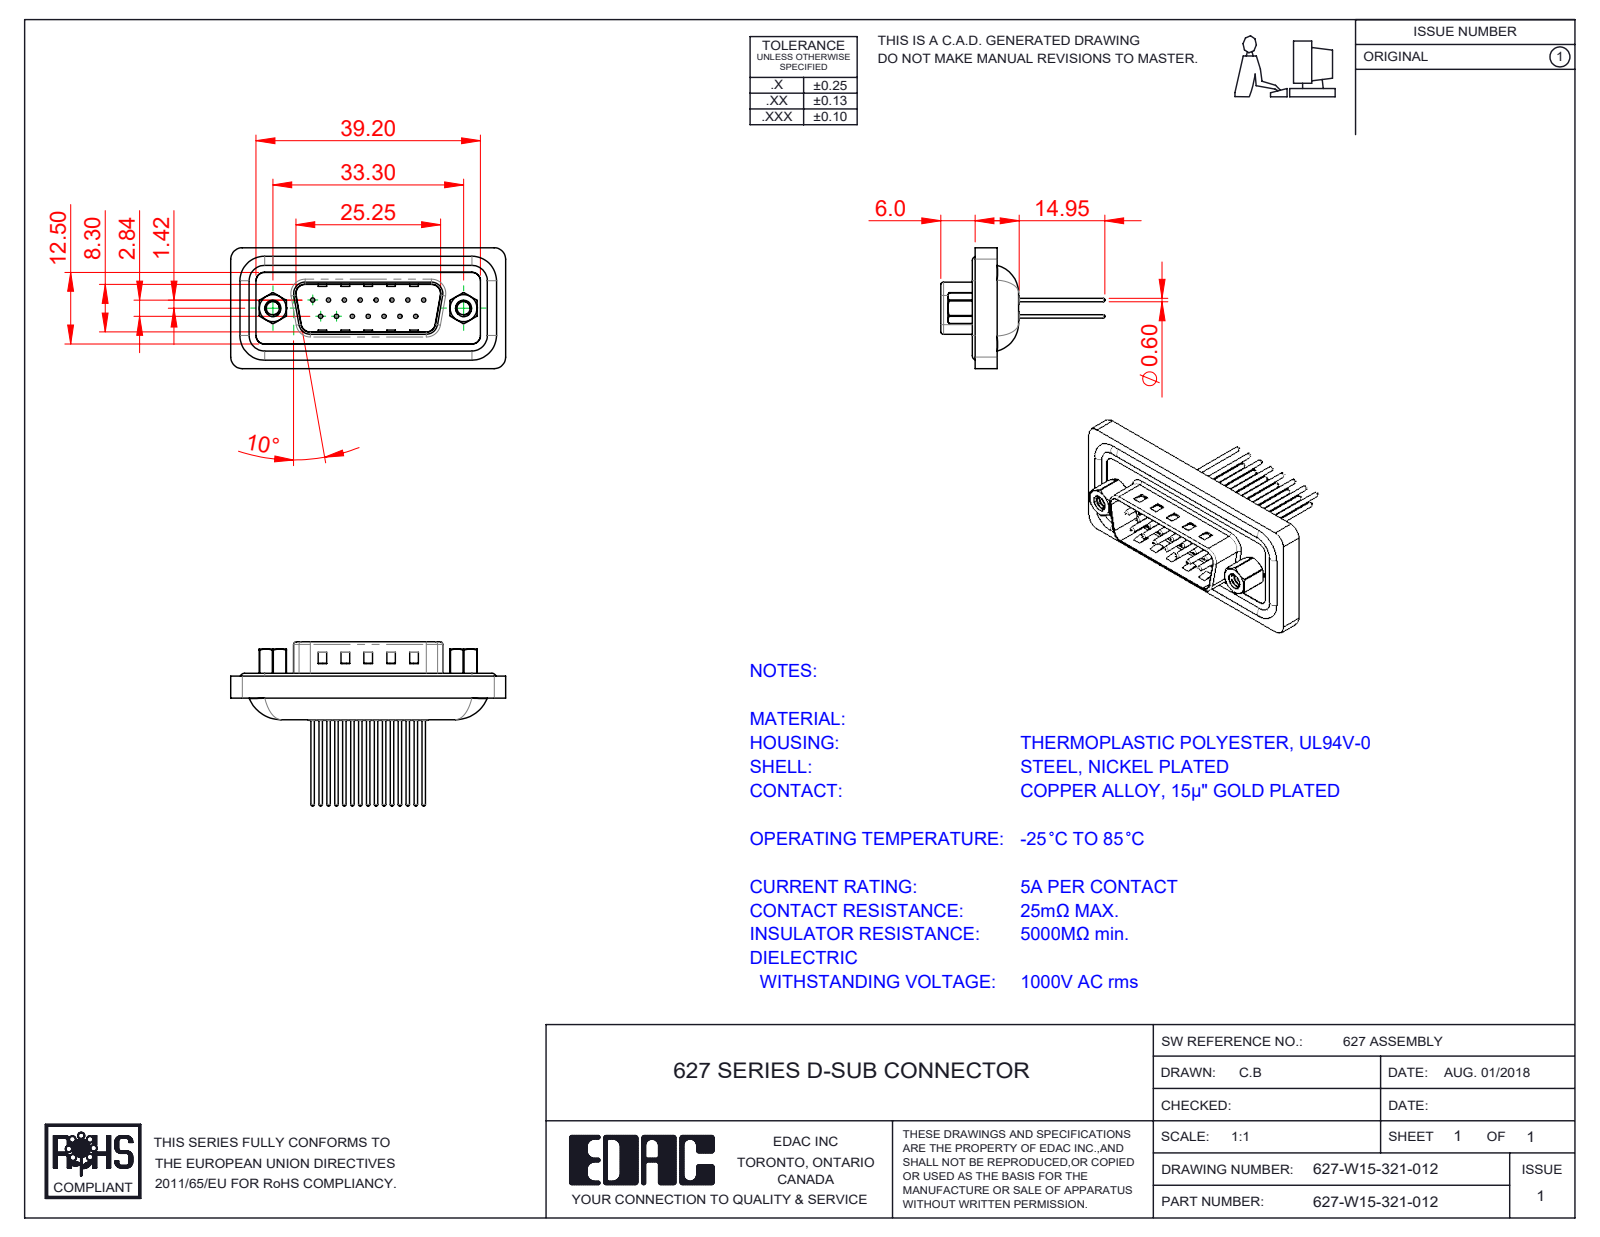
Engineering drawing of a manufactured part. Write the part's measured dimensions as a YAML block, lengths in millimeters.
part_name: "627W Contact Row 2_21; 627W 4-40 Hex Standoff; 627W 4-40 Threaded Rivet; 627-W15-321-012 (+4 more)"
step_written_by: "SolidWorks 2023 (CONFIG_CONTROL_DESIGN)"
units: millimeters
bodies: {solids: 23, faces: 1069, planar: 278, cylindrical: 456, other: 335}
overall_size: [48, 28.85, 21.1]
volume: 5804
surface_area: 8601
round_holes:
  - {diameter: 0.75, count: 15}
  - {diameter: 1.5, count: 15}
  - {diameter: 1.6, count: 15}
  - {diameter: 2, count: 15}
  - {diameter: 2.26, count: 2}
  - {diameter: 2.29, count: 2}
  - {diameter: 4, count: 2}
  - {diameter: 4.8, count: 2}
  - {diameter: 5, count: 2}
round_bosses_or_shafts:
  - {diameter: 0.6, count: 15}
  - {diameter: 1.5, count: 7}
  - {diameter: 1.6, count: 4}
  - {diameter: 4.9, count: 2}
  - {diameter: 2.79, count: 2}
partial_cylinders:
  - {radius: 2, count: 16}
  - {radius: 1.5, count: 14}
  - {radius: 0.5, count: 8}
  - {radius: 2.7, count: 6}
  - {radius: 0.9, count: 4}
  - {radius: 1.6, count: 4}
  - {radius: 4.3, count: 4}
  - {radius: 0.4, count: 2}
face_to_face_distances: [0.4, 0.75, 1.1, 2.75, 3.75, 0.5, 4.6, 1.6, 1, 4.1]
hole_center_spacings: [3.16, 2.77, 5.54, 8.31, 5.03, 5.04, 7.48, 7.49]
